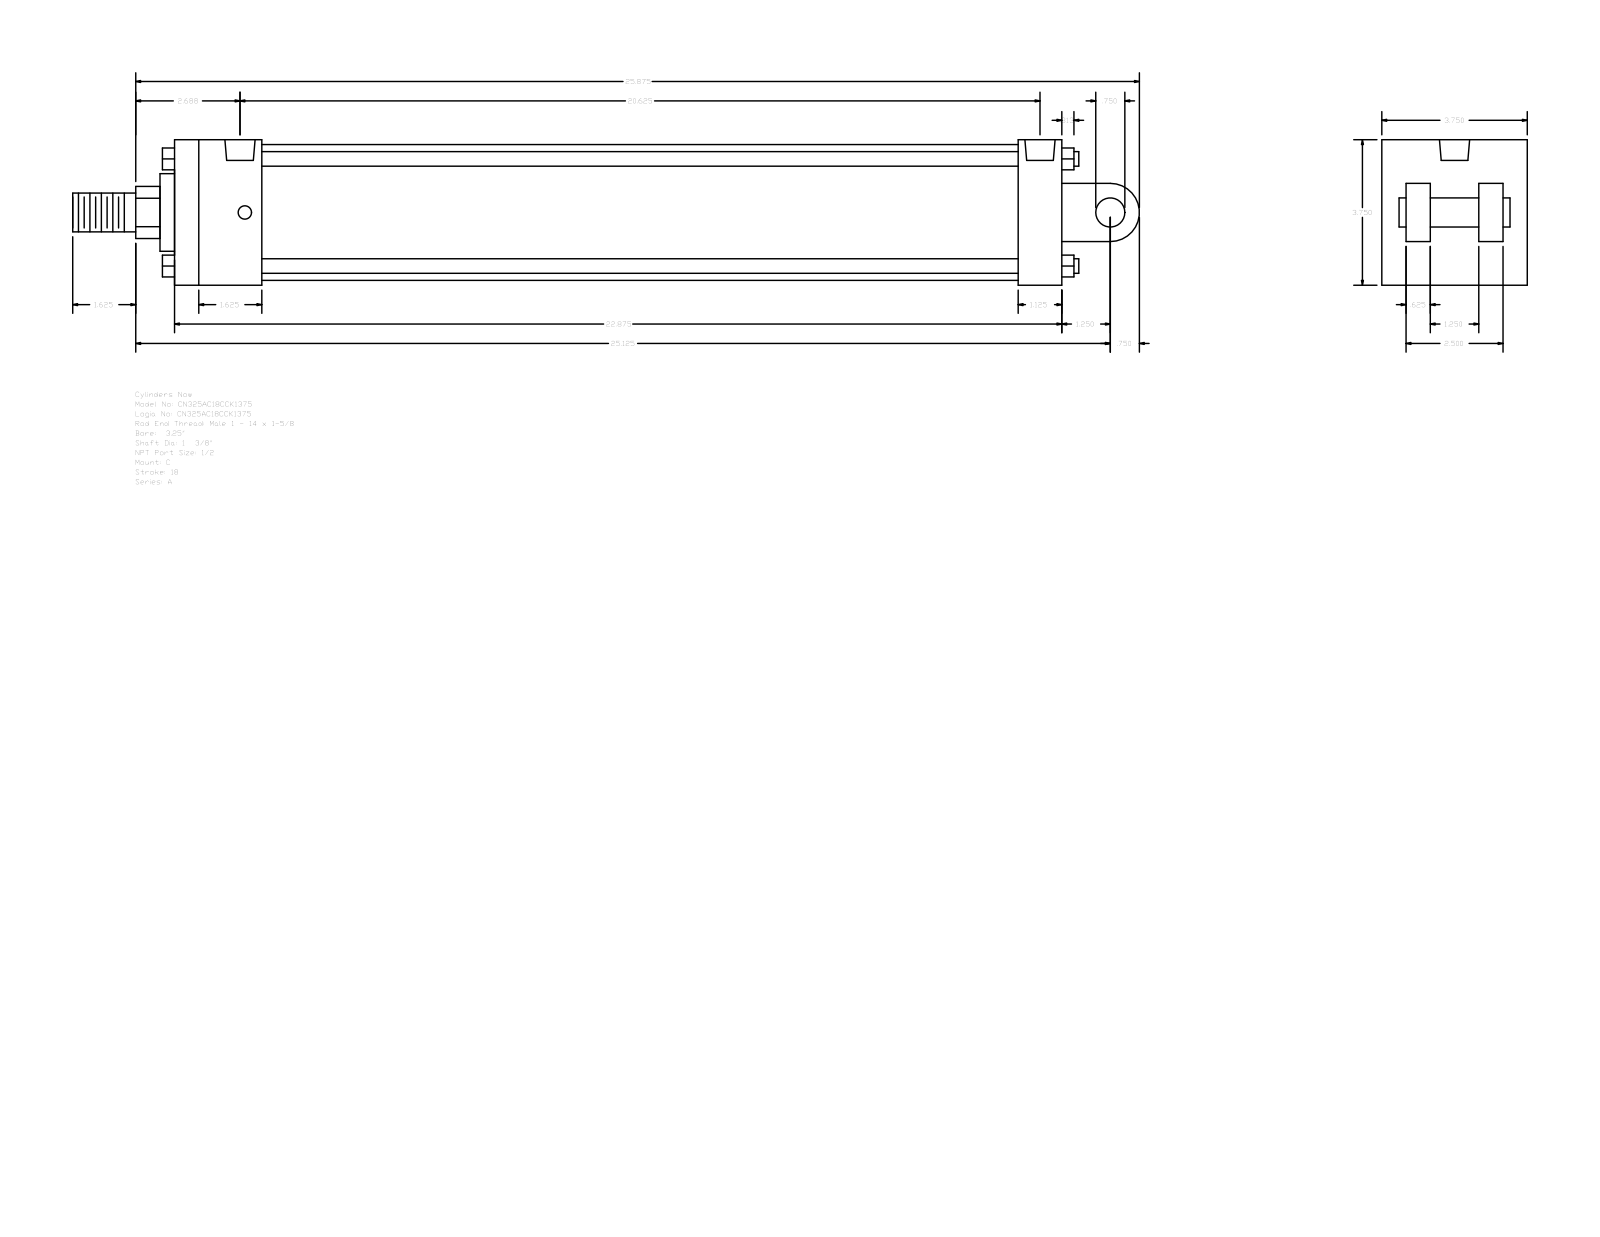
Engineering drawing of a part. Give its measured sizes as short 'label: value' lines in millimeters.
name: A_C__0325_1.375
written by: GSSL Pune (CONFIG_CONTROL_DESIGN)
unit: mm
bodies: 0 solids, 135 faces (102 planar, 33 cylindrical, 0 other)
size: 698.5 × 95.25 × 95.25
holes: 4× ⌀8.73, 2× ⌀19.77
bosses: 4× ⌀9.53, 1× ⌀88.9, 1× ⌀50.8, 1× ⌀34.92, 1× ⌀25.4, 1× ⌀19.05
rounds: 1× R17.06, 1× R19.05
face distances: 95.24, 581.02, 15.87, 28.57, 63.5, 66.67, 57.15, 31.74, 79.37, 47.63
hole spacings: 3.18, 517.52, 520.7, 523.88
